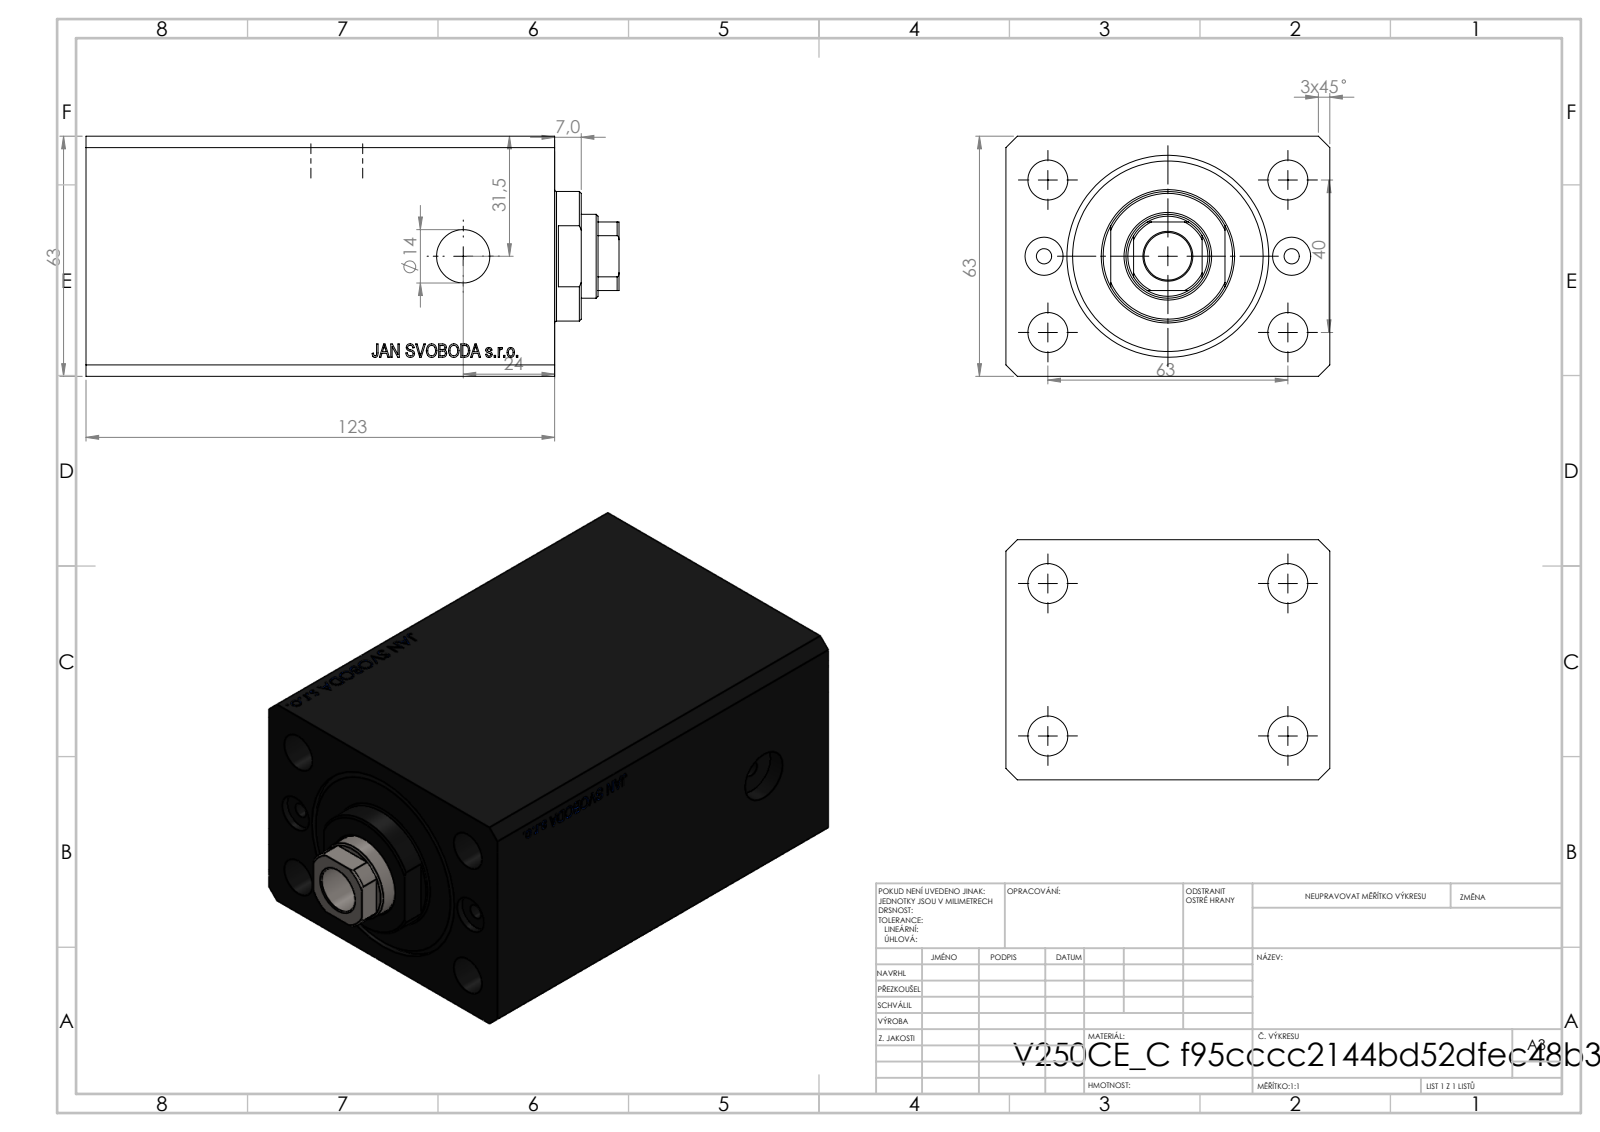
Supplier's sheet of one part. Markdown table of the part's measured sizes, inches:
| quantity | value |
| --- | --- |
| part name | V250CE_C_Body; V250CE_C_VCP; V250CE_VC_C |
| STEP written by | SolidWorks 2019 (CONFIG_CONTROL_DESIGN) |
| units | inches |
| bodies | 3 solids, 864 faces (428 planar, 44 cylindrical, 392 other) |
| overall size | 5.512 × 3.346 × 2.48 |
| volume | 35 in³ |
| surface area | 158.3 in² |
| round holes (diameter × count) | 0.157 × 4, 0.413 × 4, 0.394 × 2, 0.551 × 2, 0.492 × 1, 0.866 × 1, 1.575 × 1, 2.087 × 1 |
| round bosses / shafts (diameter × count) | 1.339 × 1 |
| partial cylindrical surfaces (radius × count) | 0.413 × 1 |
| main face-to-face distances | 2.48, 3.346, 4.843, 0.669, 4.173, 0.449, 3.724, 4.394, 3.953, 1.969 |
| hole center spacings | 0.788, 1.469, 2.64, 1.28, 1.575, 2.48, 2.938, 2.559 |
